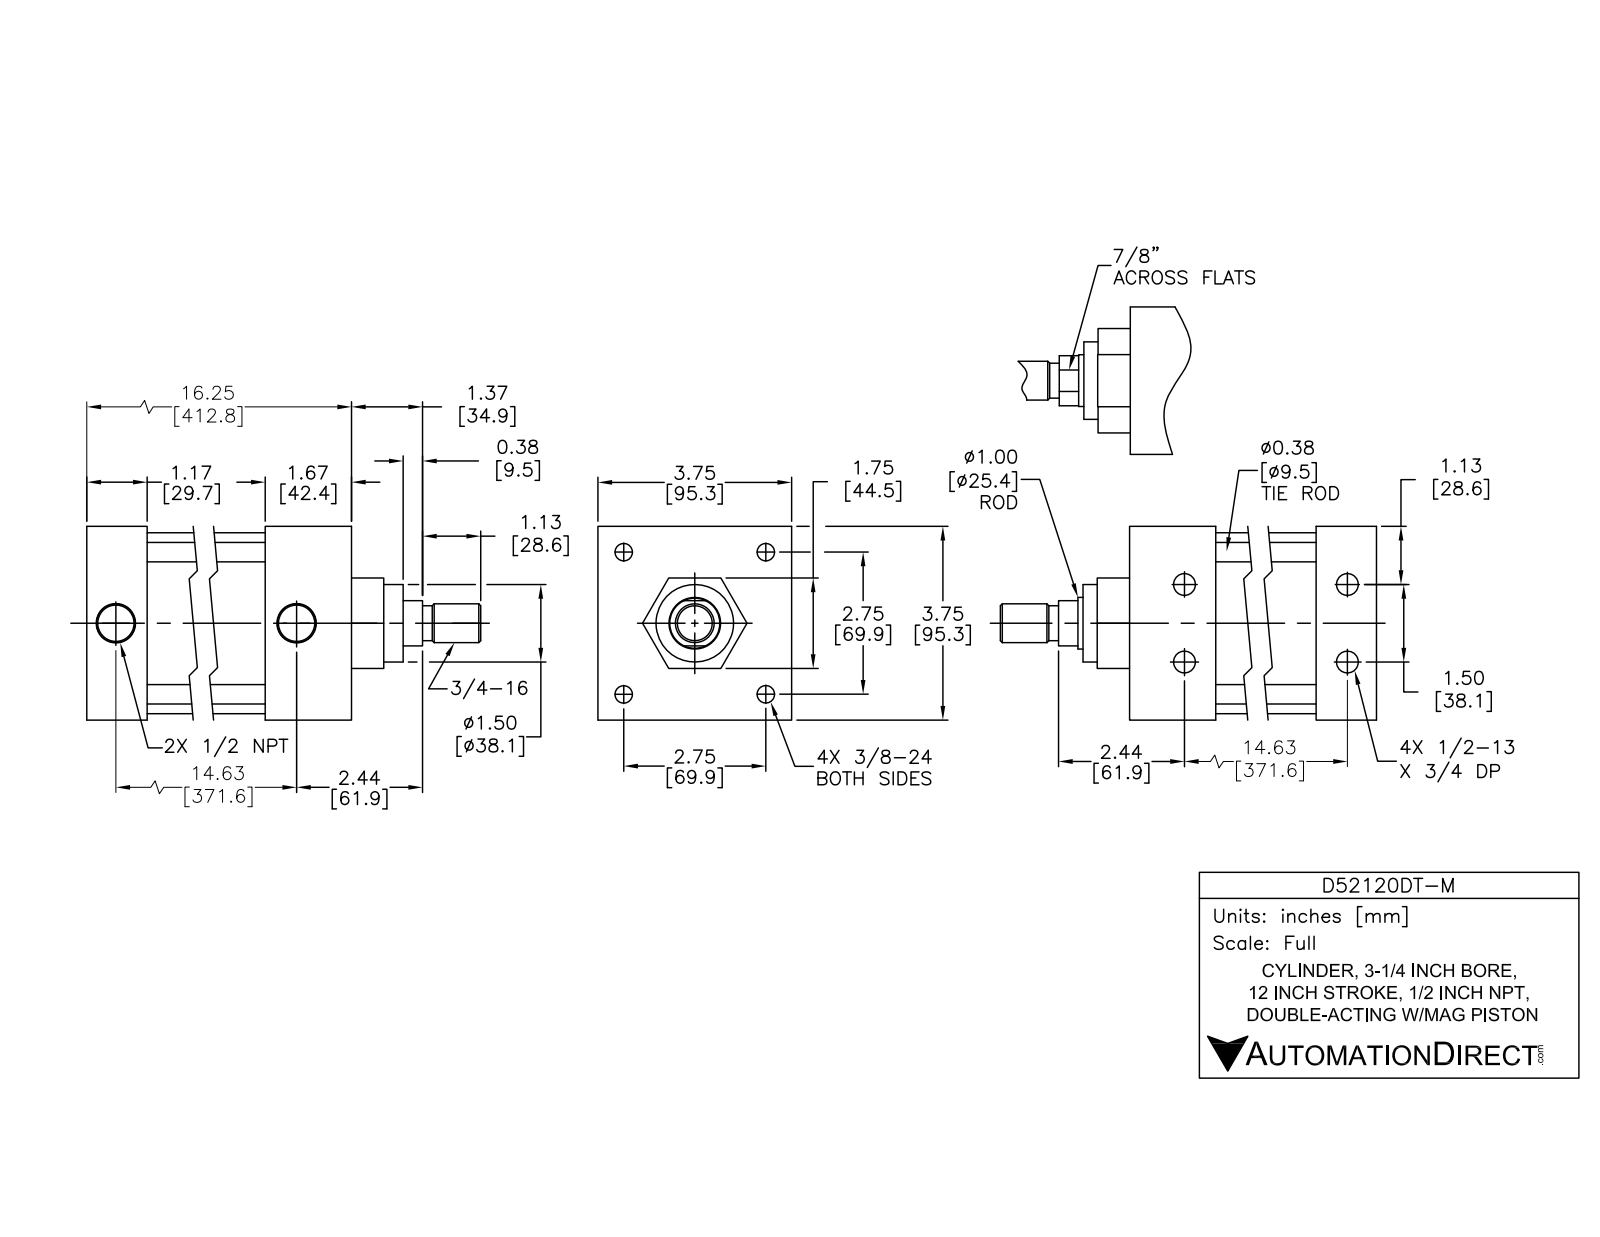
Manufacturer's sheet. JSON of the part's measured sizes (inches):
{"part_name": "D52120DT-M; D52120DT-M BODY; D52120DT-M PISTON", "step_written_by": "SolidWorks 2015 (AUTOMOTIVE_DESIGN)", "units": "inches", "bodies": {"solids": 12, "faces": 303, "planar": 99, "cylindrical": 114, "other": 90}, "overall_size": [18.745, 3.75, 3.75], "volume_in3": 83.46, "surface_area_in2": 580.4, "round_holes": [[0.33, 4], [0.406, 4], [0.417, 4], [0.625, 4], [0.5, 2], [0.766, 2], [1, 1], [1.003, 1], [3.25, 1]], "round_bosses_or_shafts": [[0.609, 4], [0.375, 4], [0.34, 4], [3.5, 1], [3.247, 1], [1.75, 1], [0.997, 1], [0.97, 1]], "partial_cylinders_radius": [[0.375, 4]], "face_to_face_distances": [3.75, 16.246, 1.75, 14.997, 1.249, 13.751, 1.246, 2.495, 14.996, 1.245], "hole_center_spacings": [0.75, 0.76, 1.5, 1.95, 1.95, 2.758, 2.758, 3.9]}
